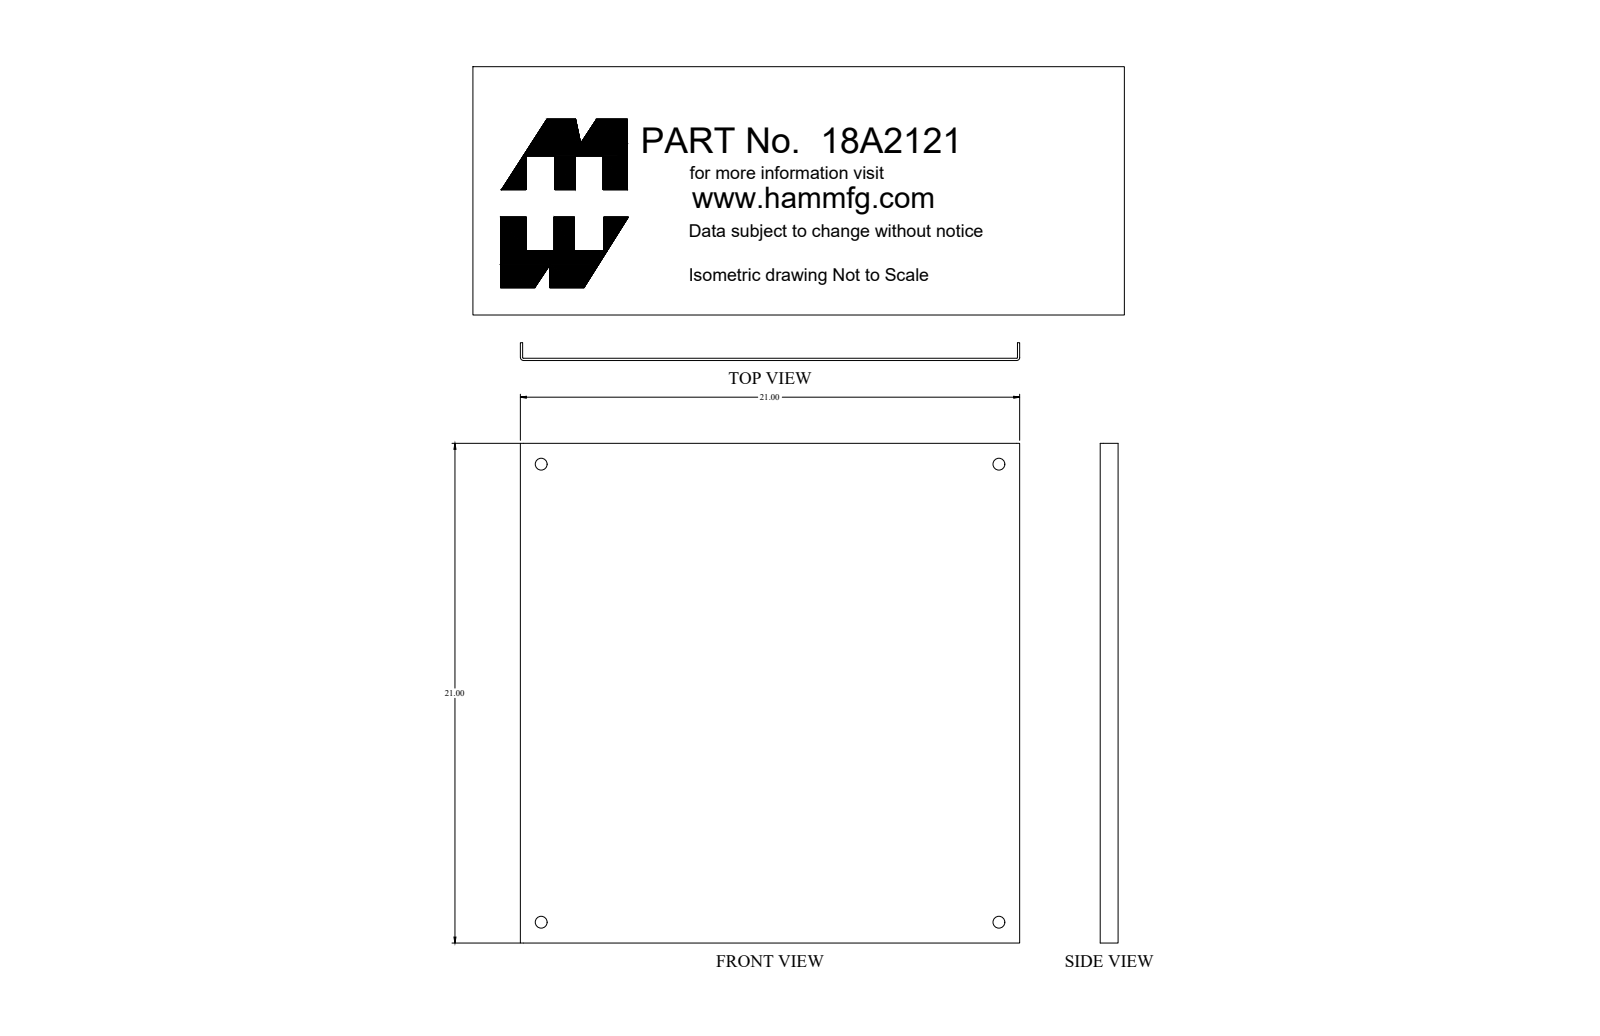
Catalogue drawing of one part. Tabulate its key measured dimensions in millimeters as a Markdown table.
| quantity | value |
| --- | --- |
| part name | 18A2121 |
| STEP written by | SolidWorks 2018 (AUTOMOTIVE_DESIGN) |
| units | millimeters |
| bodies | 1 solid, 18 faces (10 planar, 8 cylindrical, 0 other) |
| overall size | 533.4 × 533.4 × 19.1 |
| volume | 725 900 mm³ |
| surface area | 607 400 mm² |
| round holes (diameter × count) | 12.7 × 4 |
| partial cylindrical surfaces (radius × count) | 0.8 × 2, 3.2 × 2 |
| main face-to-face distances | 2.4, 531, 533.4, 528.6, 19.1, 16.6 |
| hole center spacings | 489, 691.5 |
